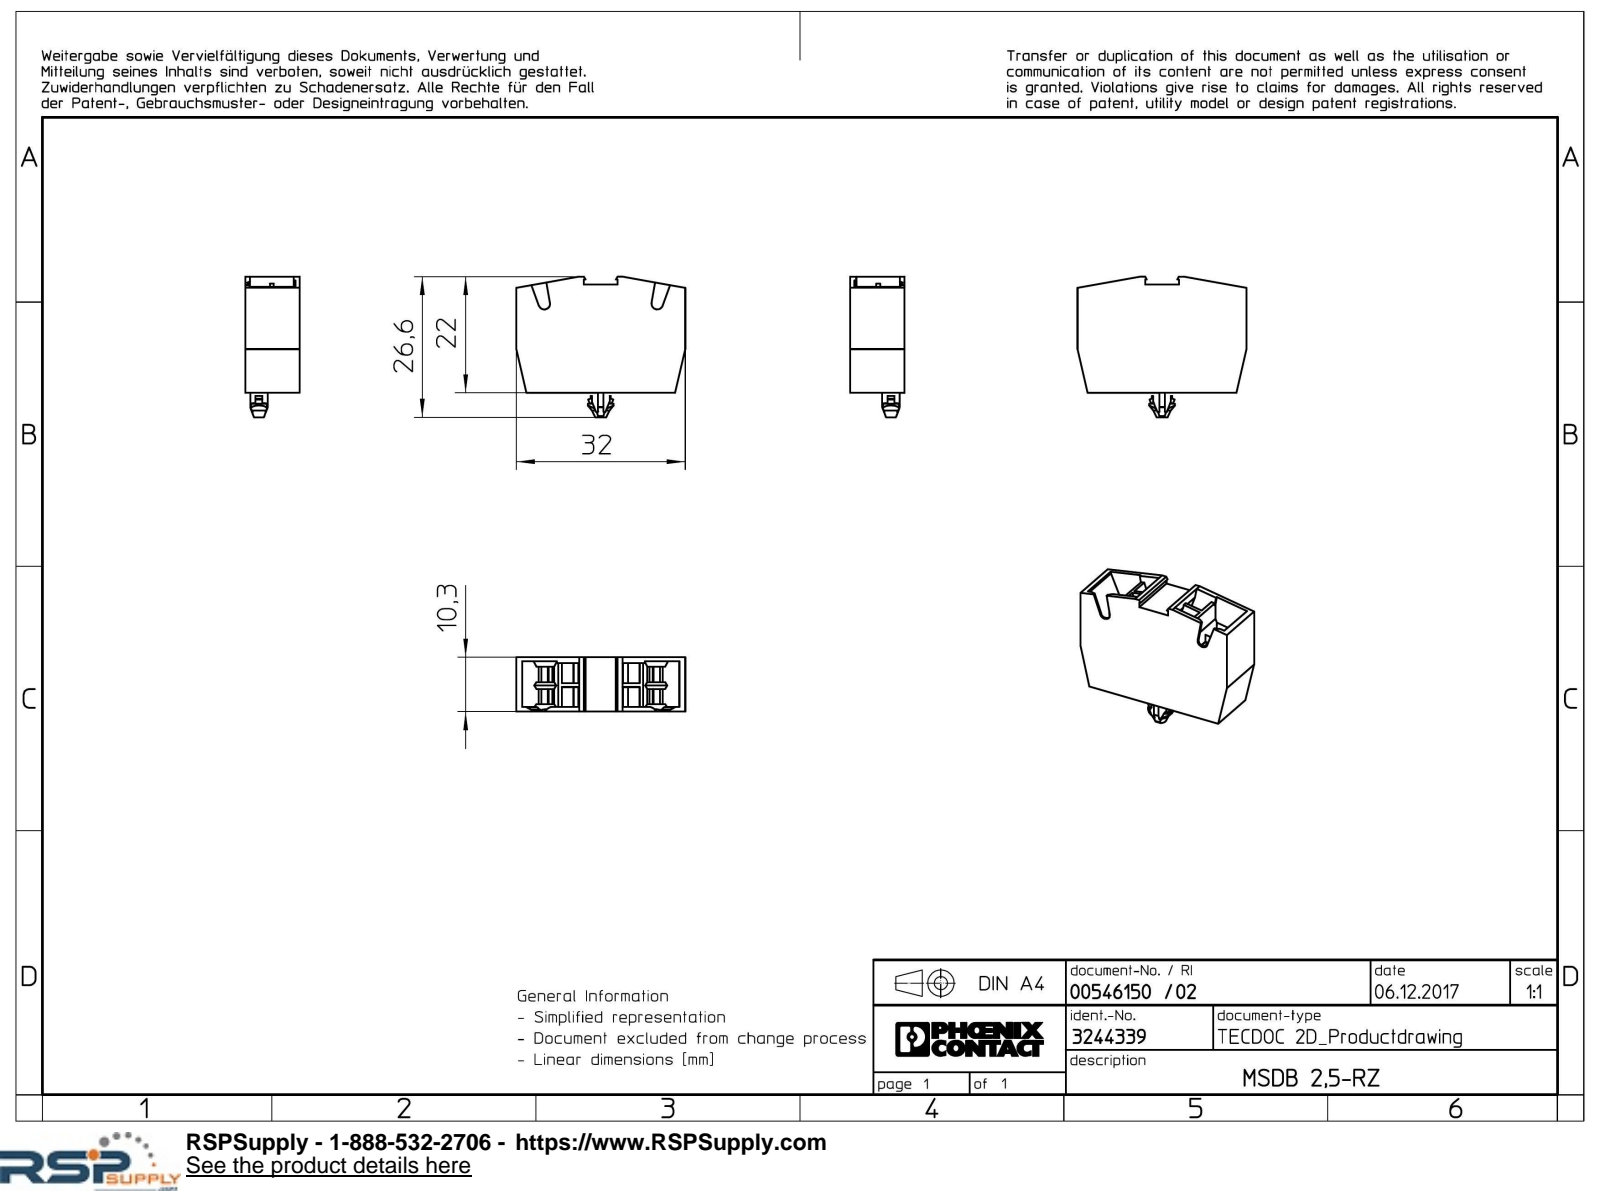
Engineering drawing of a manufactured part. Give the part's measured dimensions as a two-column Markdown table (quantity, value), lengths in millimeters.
| quantity | value |
| --- | --- |
| part name | MSDB_2.5_RZ_select |
| STEP written by | Creo Elements/Direct Modeling 20.1A 29-Sep-2018 (C) Parametric Technology GmbH (AUTOMOTIVE_DESIGN) |
| units | millimeters |
| bodies | 1 solid, 181 faces (153 planar, 18 cylindrical, 10 other) |
| overall size | 32 × 26.6 × 10.3 |
| volume | 5 215 mm³ |
| surface area | 3 773 mm² |
| partial cylindrical surfaces (radius × count) | 1 × 8, 0.2 × 4, 1.6 × 2, 2.4 × 2, 2.62 × 2 |
| main face-to-face distances | 10.3, 3.75, 4.5, 0.9, 3.4, 32, 0.35, 4.85, 9.4, 4.78 |
